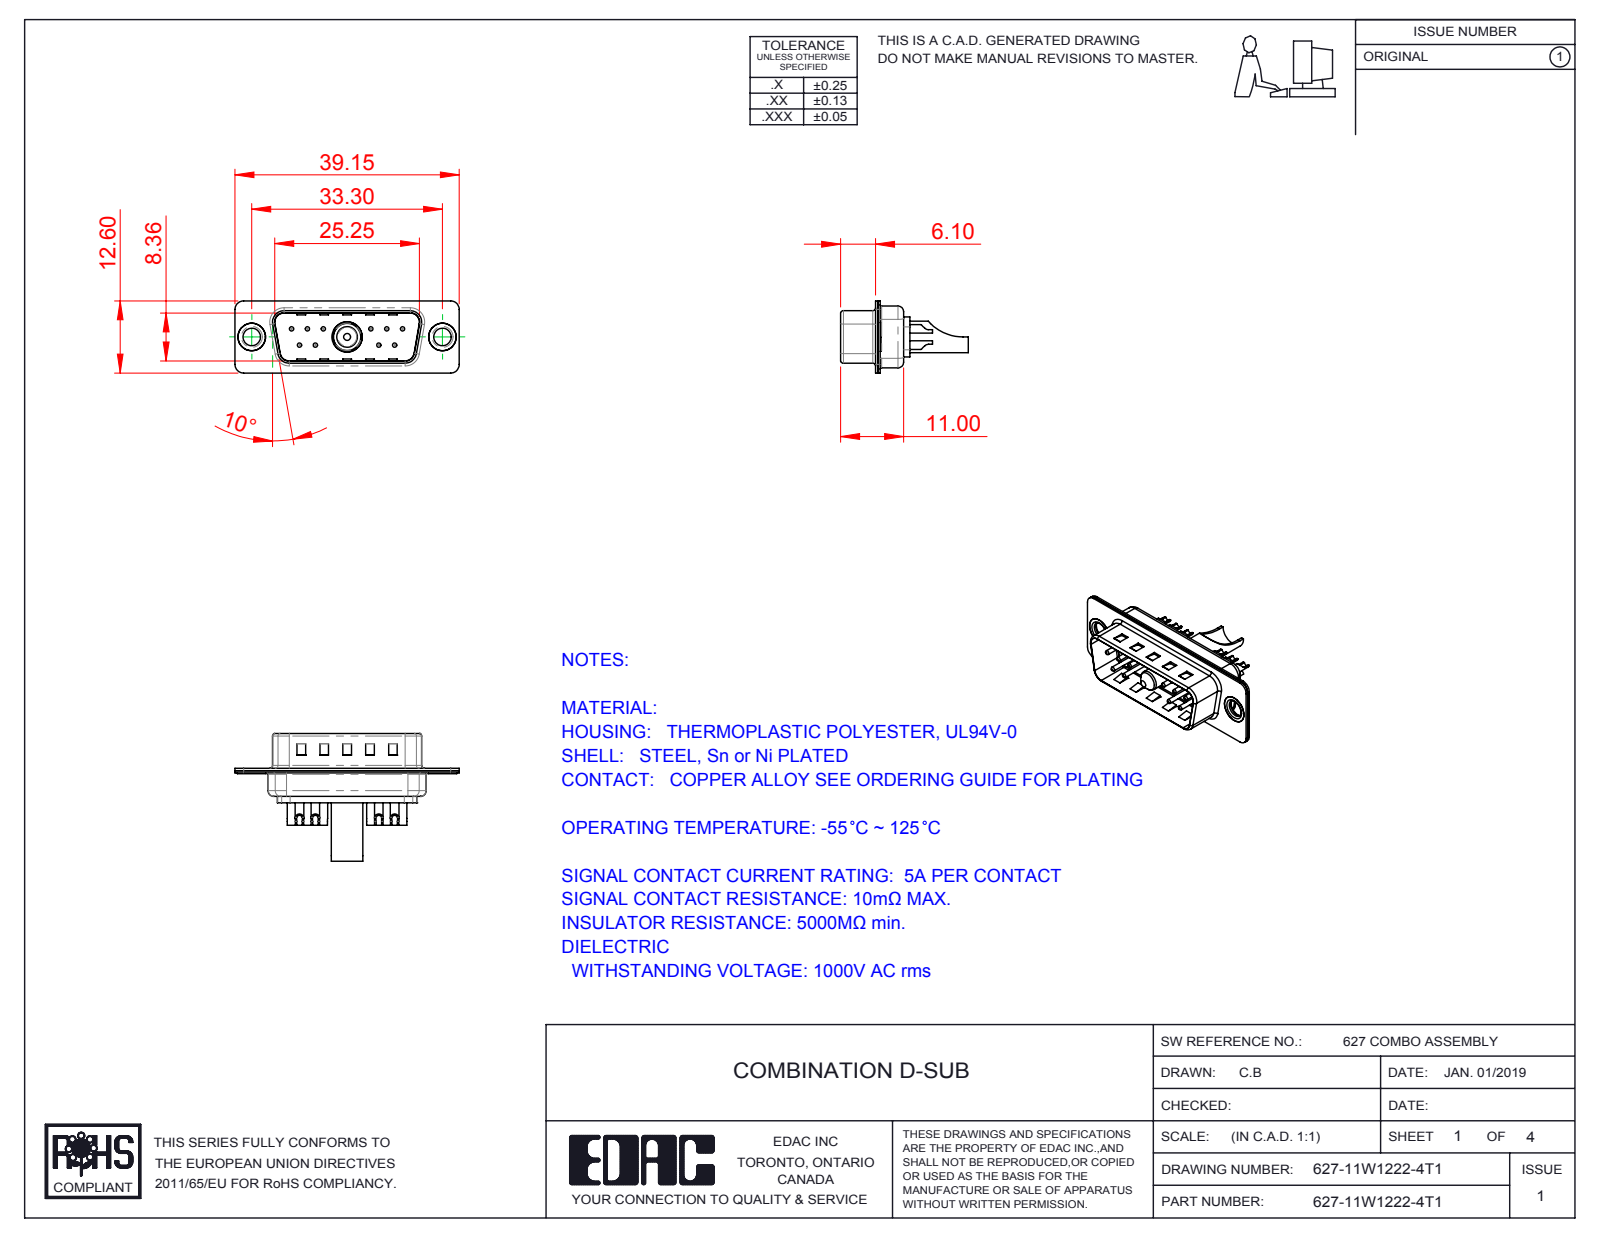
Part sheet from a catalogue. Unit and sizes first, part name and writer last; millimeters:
Units: millimetres
Overall size (bounding box): 39.15 × 22.3 × 12.6
Round holes (diameter × count): ⌀0.75 ×10, ⌀1 ×10, ⌀1.6 ×10, ⌀2 ×10, ⌀3.05 ×2, ⌀4 ×2, ⌀4.8 ×2, ⌀4.6 ×1, ⌀4.85 ×1, ⌀5.3 ×1
Round bosses / shafts (diameter × count): ⌀1.5 ×10, ⌀5 ×2, ⌀4.9 ×2, ⌀3.55 ×2, ⌀5.5 ×1, ⌀5.2 ×1, ⌀4.75 ×1, ⌀3.75 ×1
Partial cylindrical surfaces — rounded edges, fillets, slot ends (radius × count): R1.5 ×20, R2 ×12, R1 ×9, R0.5 ×8, R1.6 ×8, R0.25 ×4, R0.6 ×4, R0.65 ×4
Main face-to-face distances: 0.4, 0.82, 9.58, 0.8, 8.76, 1.5, 5.2, 5.6, 6, 1.22
Hole centre spacings: 3.16, 2.77, 13.85, 11.08, 16.62, 5.03, 5.04, 5.54
Volume: 1 889 mm³ · Surface area: 4 864 mm²
Bodies: 17 solids, 740 faces (250 planar, 301 cylindrical, 189 other)
Part name (STEP PRODUCT): 627Combo Housing_11W1; Power Pin_40A SC; 627Combo Shell Front_15 Contacts; 627Combo Thru Hole Rivet (+4 more)
STEP written by: SolidWorks 2016 (CONFIG_CONTROL_DESIGN)
